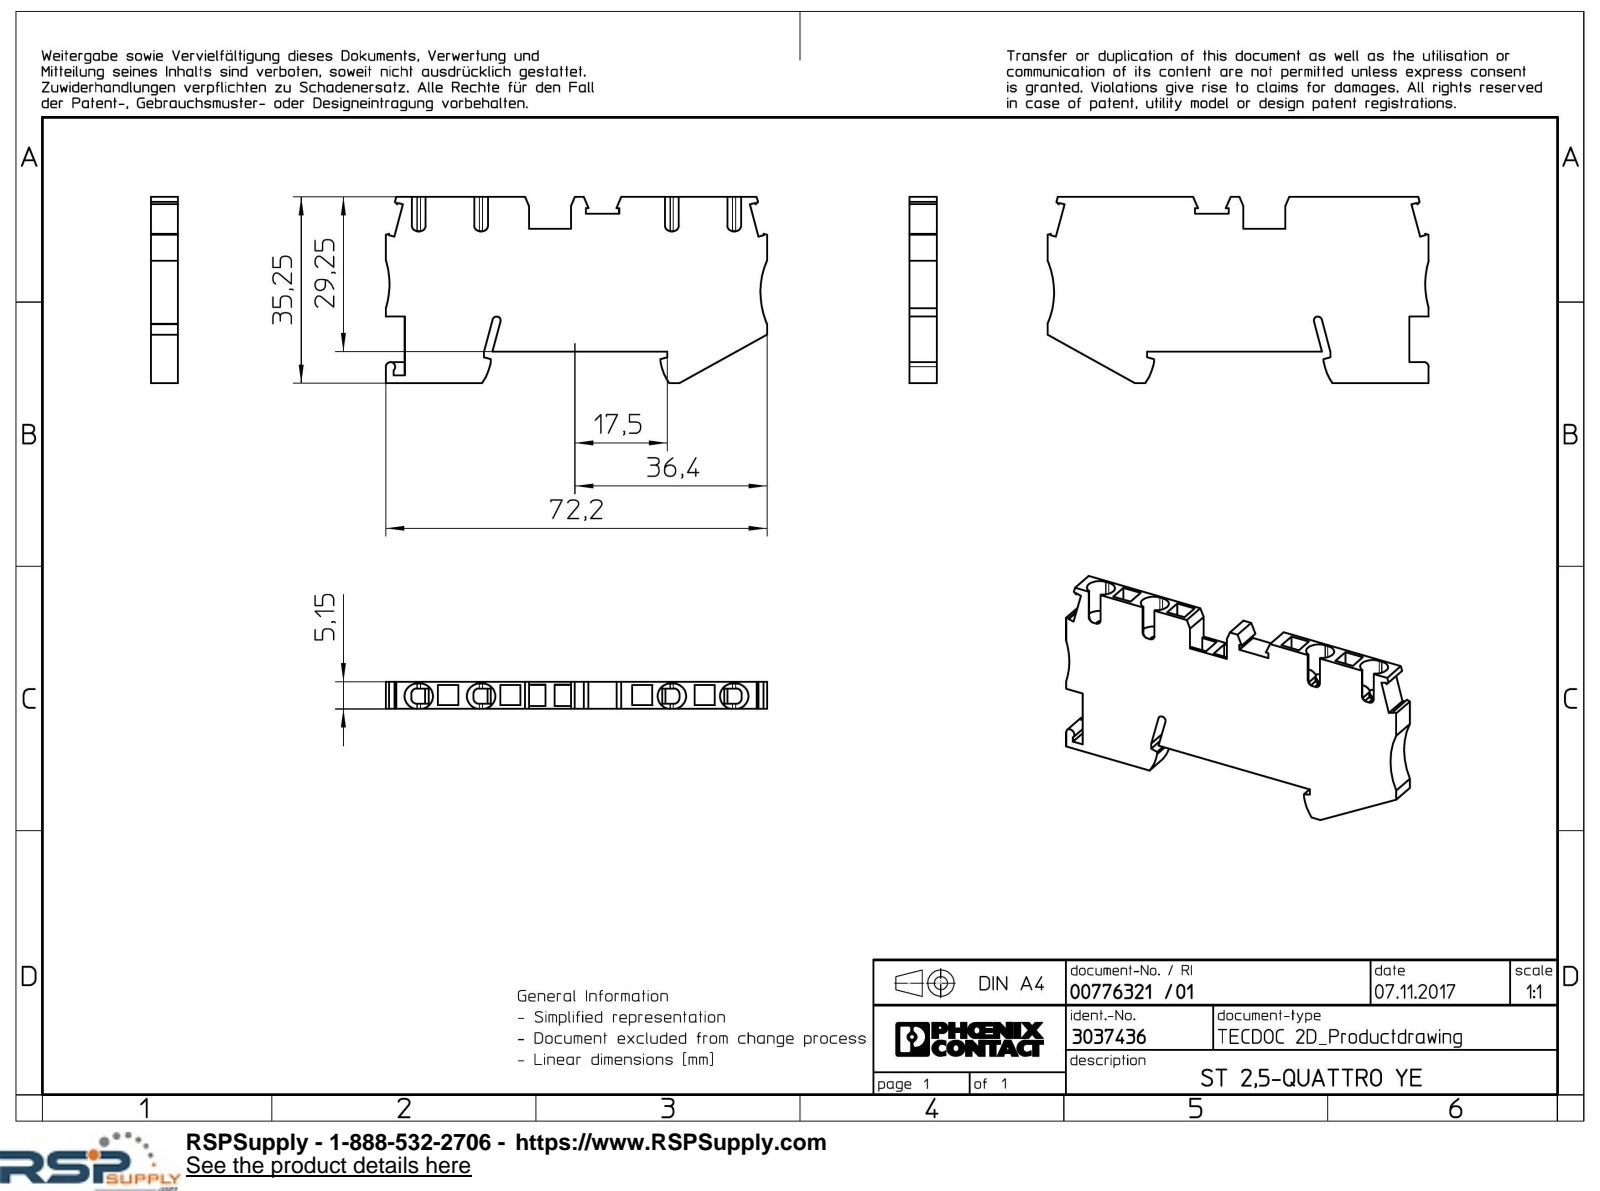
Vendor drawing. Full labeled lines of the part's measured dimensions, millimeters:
Part name (STEP PRODUCT): ST_2.5-QUATTRO_YE-select
STEP written by: Creo Elements/Direct Modeling 20.1A 29-Sep-2018 (C) Parametric Technology GmbH (AUTOMOTIVE_DESIGN)
Units: millimetres
Bodies: 1 solid, 181 faces (138 planar, 31 cylindrical, 12 other)
Overall size (bounding box): 72.2 × 35.25 × 5.15
Volume: 9 313 mm³ · Surface area: 7 014 mm²
Partial cylindrical surfaces — rounded edges, fillets, slot ends (radius × count): R1 ×16, R2.4 ×8, R9.5 ×2, R15 ×2, R0.7 ×1, R0.8 ×1, R0.9 ×1
Main face-to-face distances: 5.15, 3.8, 3.15, 0.65, 29.25, 11.8, 6, 4.45, 8, 35.25
